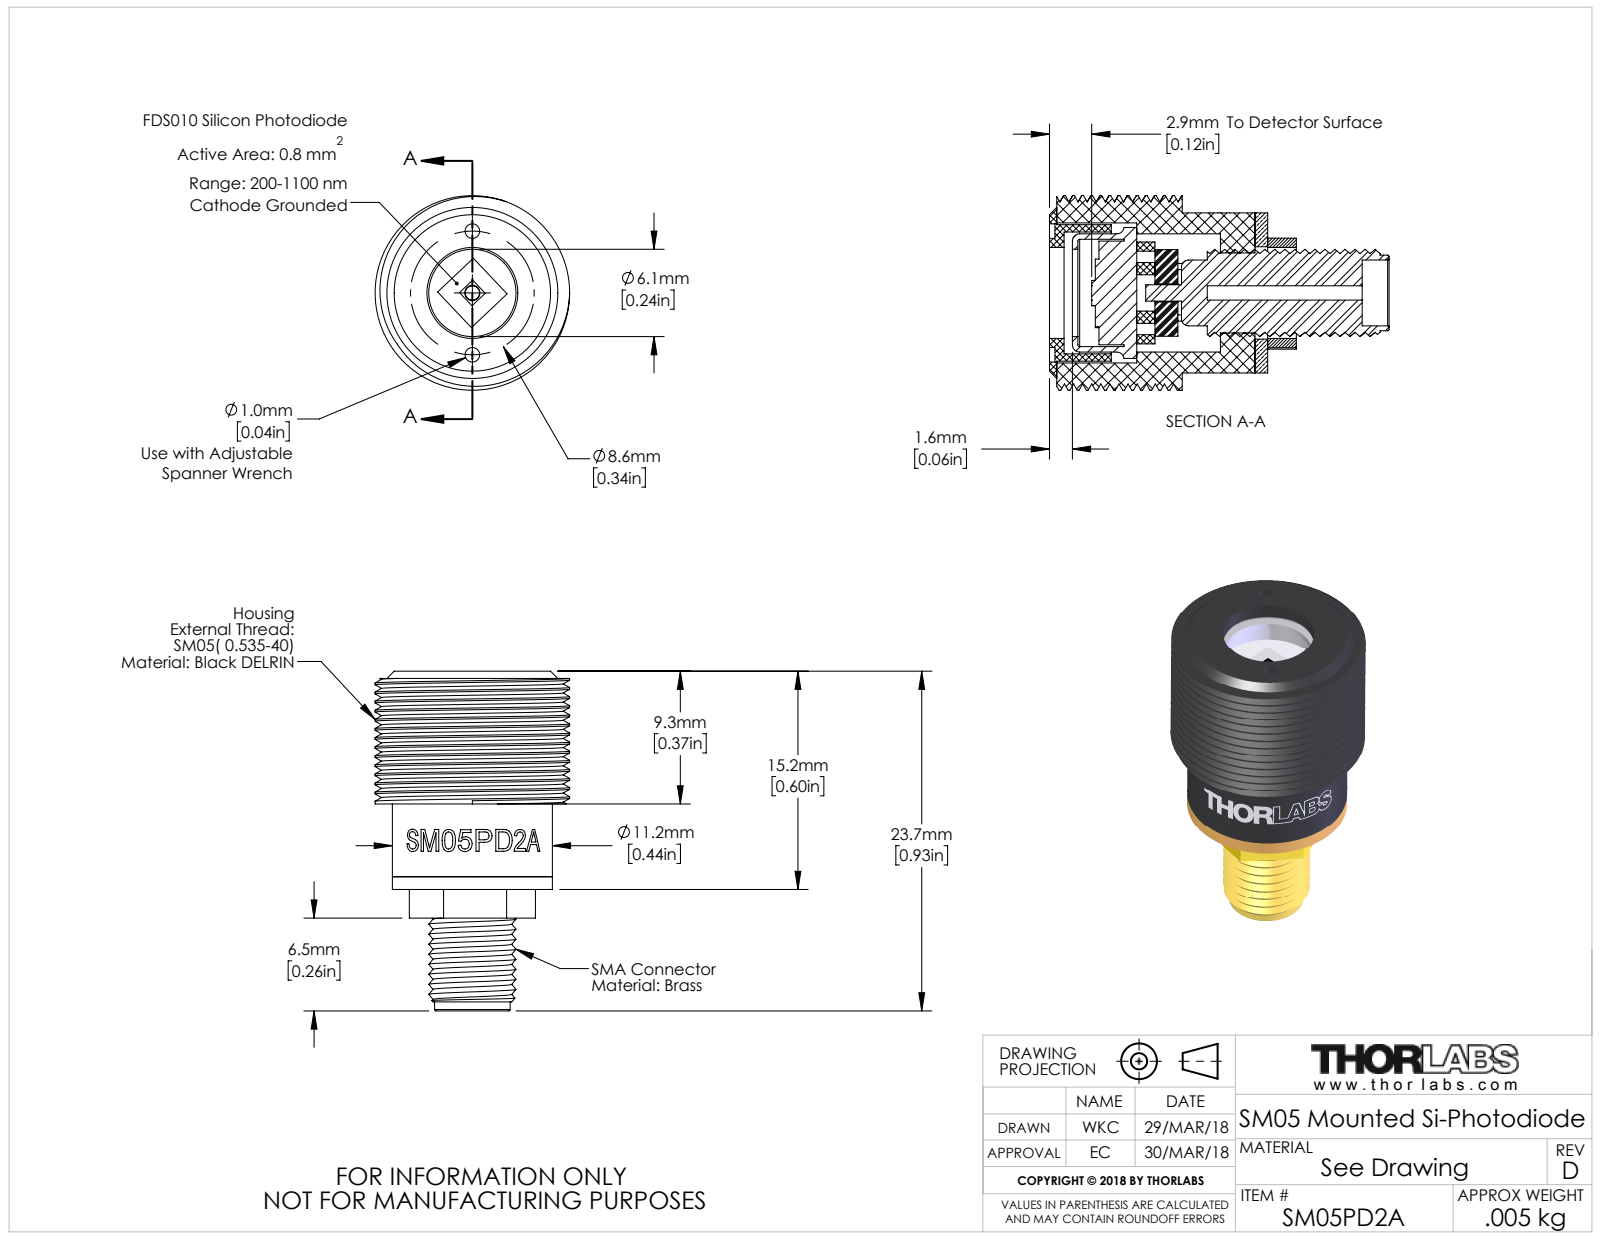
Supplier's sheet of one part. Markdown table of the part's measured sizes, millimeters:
| quantity | value |
| --- | --- |
| part name | 8920-E0W |
| STEP written by | SolidWorks 2016 (AUTOMOTIVE_DESIGN) |
| units | millimeters |
| bodies | 6 solids, 149 faces (55 planar, 66 cylindrical, 28 other) |
| overall size | 23.5 × 13.6 × 13.6 |
| volume | 1 600 mm³ |
| surface area | 2 899 mm² |
| round holes (diameter × count) | 1 × 2, 1.7 × 2, 1 × 1, 1 × 1, 4.6 × 1, 5.6 × 1, 6.1 × 1, 6.4 × 1, 6.5 × 1, 7.5 × 1, 8.3 × 1, 8.5 × 1 |
| round bosses / shafts (diameter × count) | 0.4 × 3, 13.6 × 1, 11.2 × 1, 9.5 × 1, 9.1 × 1, 8.3 × 1, 7.2 × 1, 5.3 × 1 |
| partial cylindrical surfaces (radius × count) | 0.1 × 10 |
| main face-to-face distances | 0.9, 0.5, 9.4, 14.7, 13.8, 8.5, 5.3, 15.2, 14.4, 5.8 |
| hole center spacings | 2.5, 4.3, 1.8, 3.6, 4.9, 5.1, 6.9, 8.6 |
